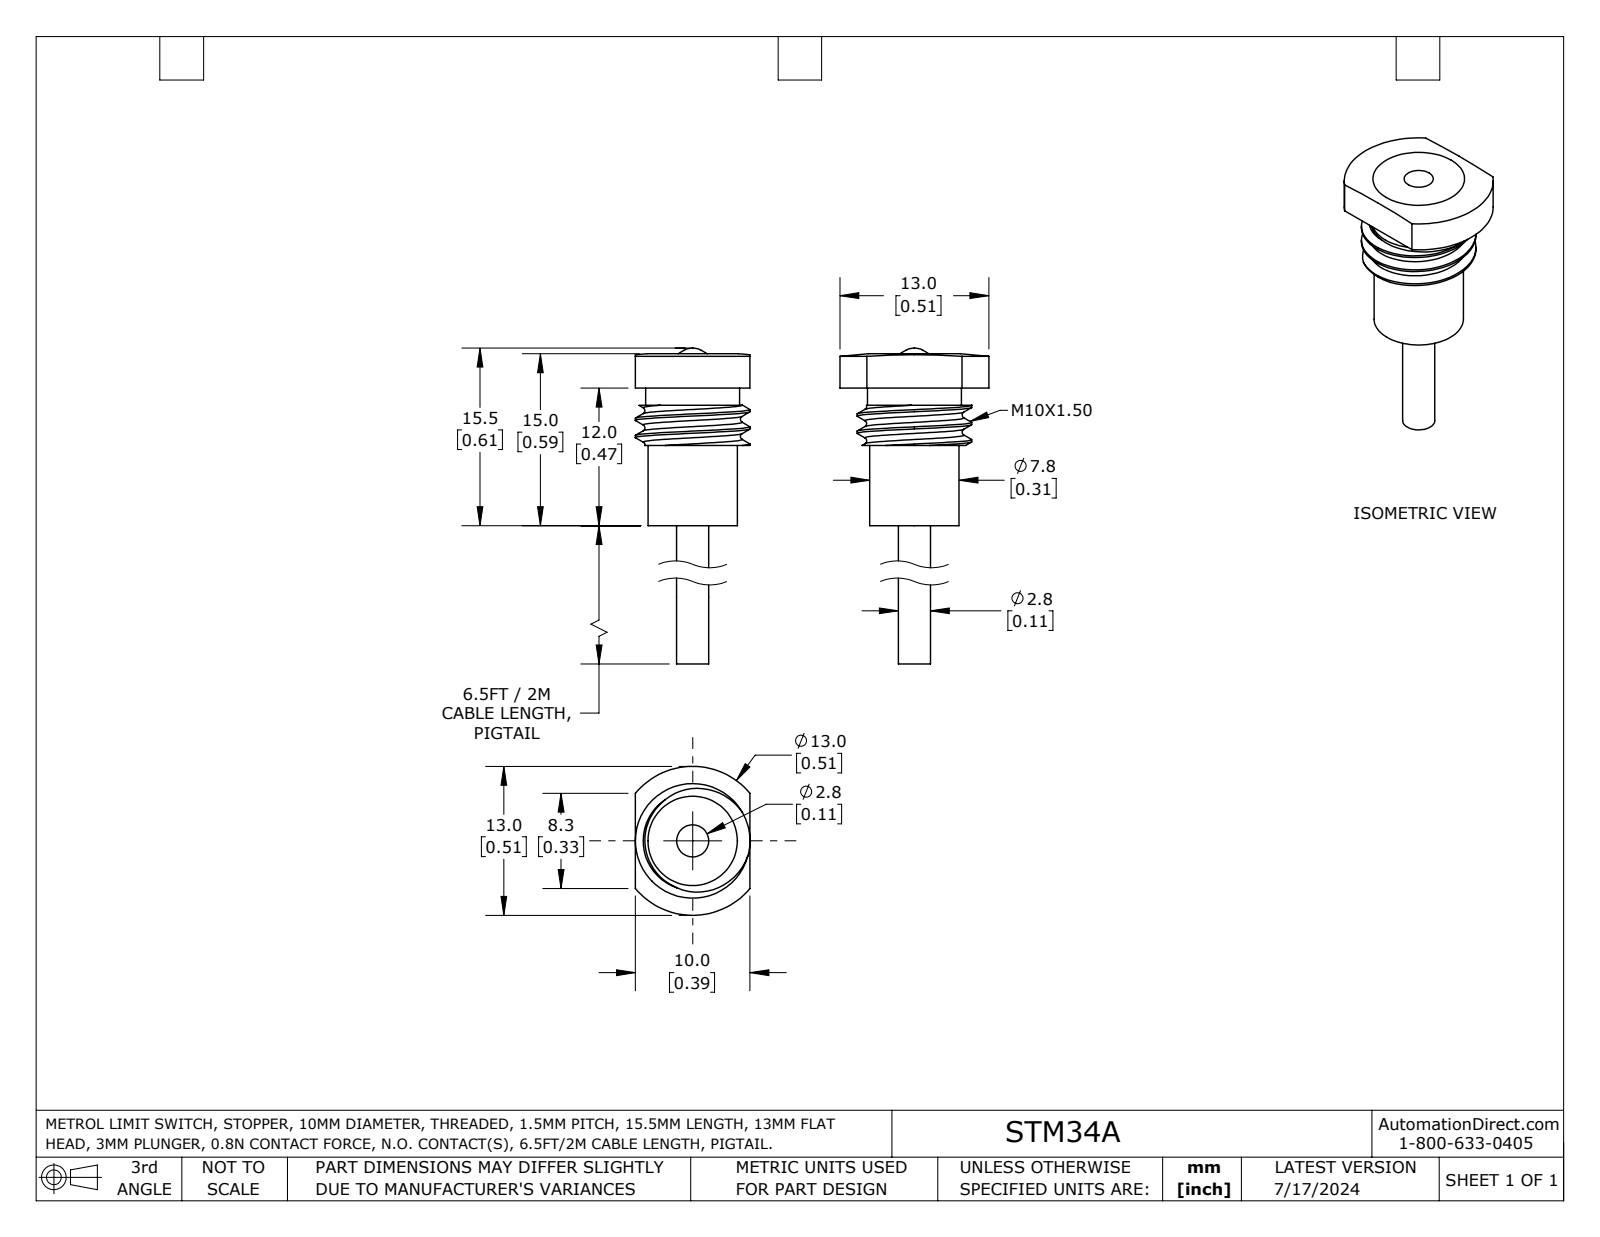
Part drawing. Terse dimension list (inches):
name: STM34A
written by: SolidWorks 2023 (AUTOMOTIVE_DESIGN)
unit: in
bodies: 1 solid, 31 faces (8 planar, 14 cylindrical, 9 other)
size: 0.807 × 0.512 × 0.394
volume: 0.062 in³; area: 1.213 in²
bosses: 1× ⌀0.394, 1× ⌀0.323, 1× ⌀0.307, 1× ⌀0.11
rounds: 1× R0.256
face distances: 0.472, 0.118, 0.591, 0.394, 0.197, 0.276, 0.315, 0.413, 0.138, 0.059
